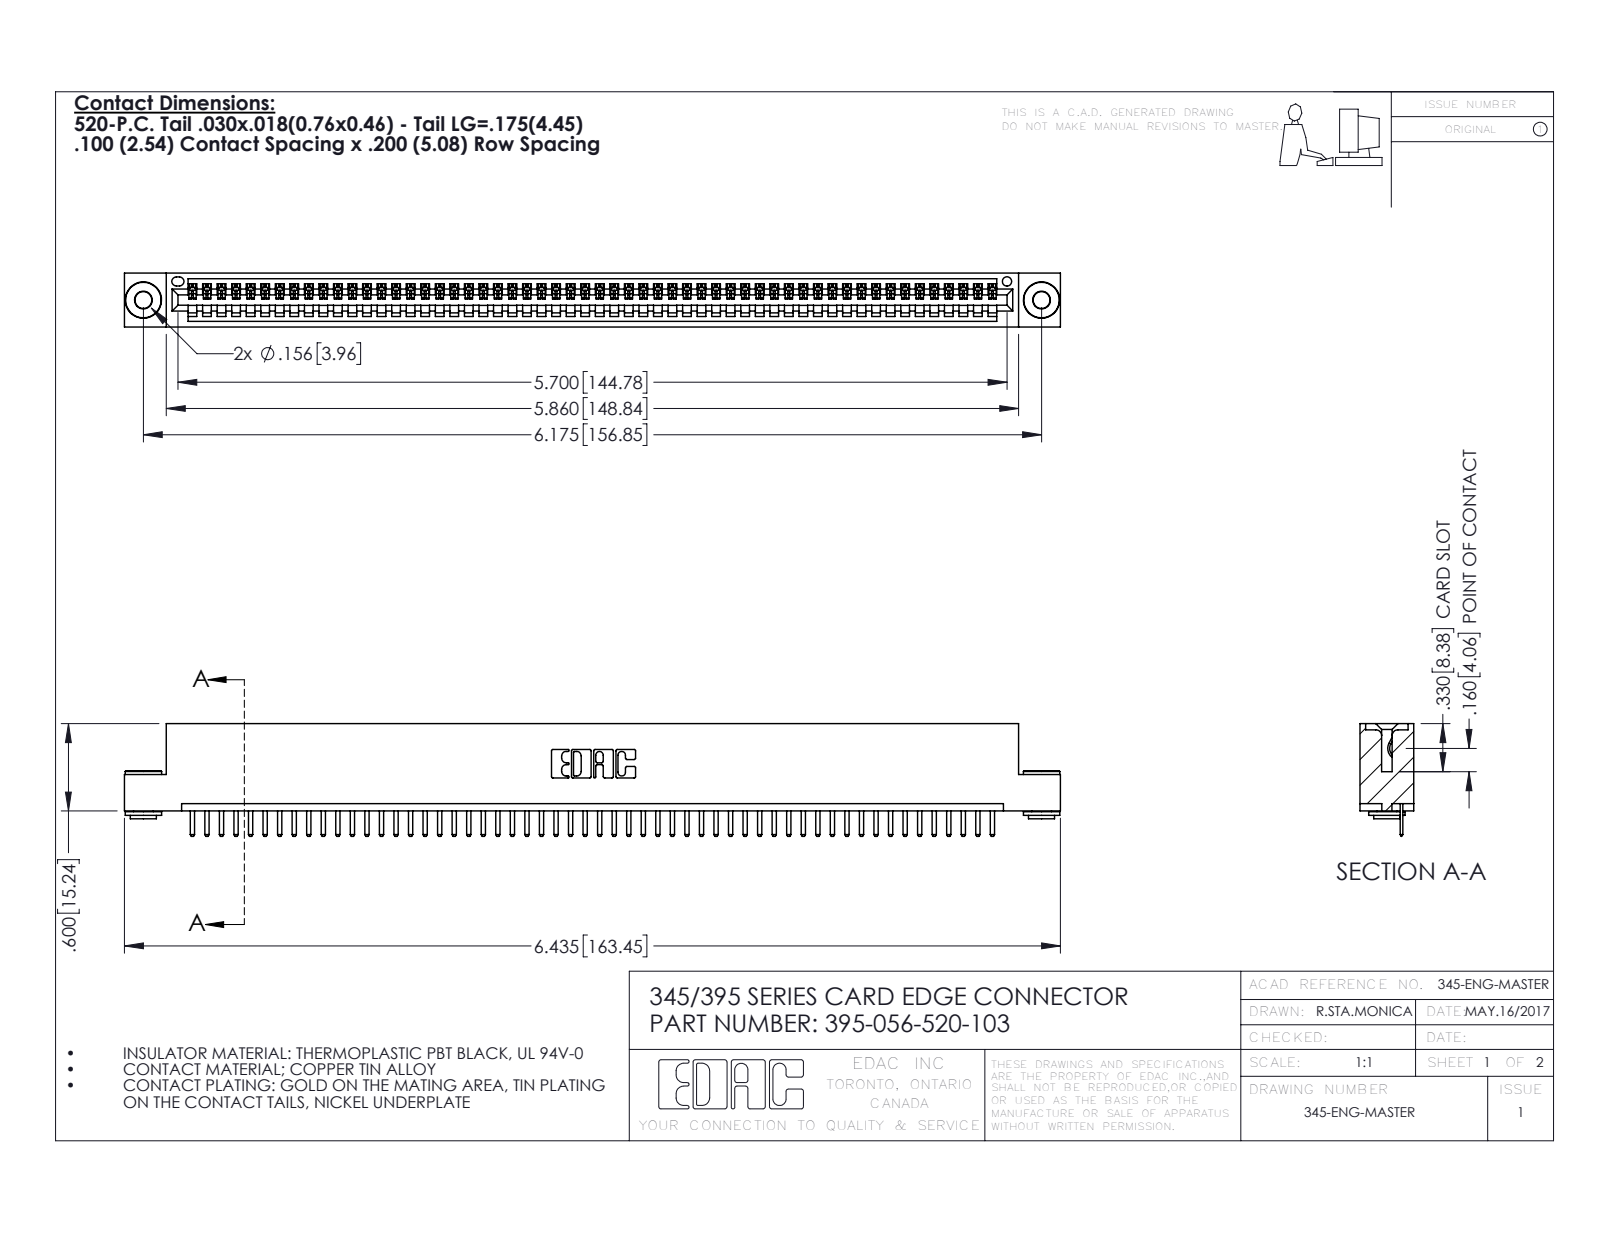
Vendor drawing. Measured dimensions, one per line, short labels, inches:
name: 345-250-002_345-250-002-102; 345 Part_Flush Mounting Lugs - 0.156 Dia-TH; 395-056-520-103; 345-292-001_345-293-120
written by: SolidWorks 2016 (CONFIG_CONTROL_DESIGN)
unit: in
bodies: 59 solids, 3636 faces (2442 planar, 1186 cylindrical, 8 other)
size: 6.435 × 0.775 × 0.37
volume: 0.946 in³; area: 31.73 in²
holes: 2× ⌀0.116, 2× ⌀0.156, 1× ⌀0.064
bosses: 2× ⌀0.25, 2× ⌀0.18, 2× ⌀0.136
rounds: 114× R0.01, 112× R0.006, 22× R0.01, 6× R0.007, 6× R0.031, 3× R0.026, 2× R0.031, 2× R0.04
face distances: 0.072, 0.298, 0.37, 0.2, 0.025, 0.098, 0.272, 0.225, 0.072, 0.149
hole spacings: 0.27, 5.939, 6.175
